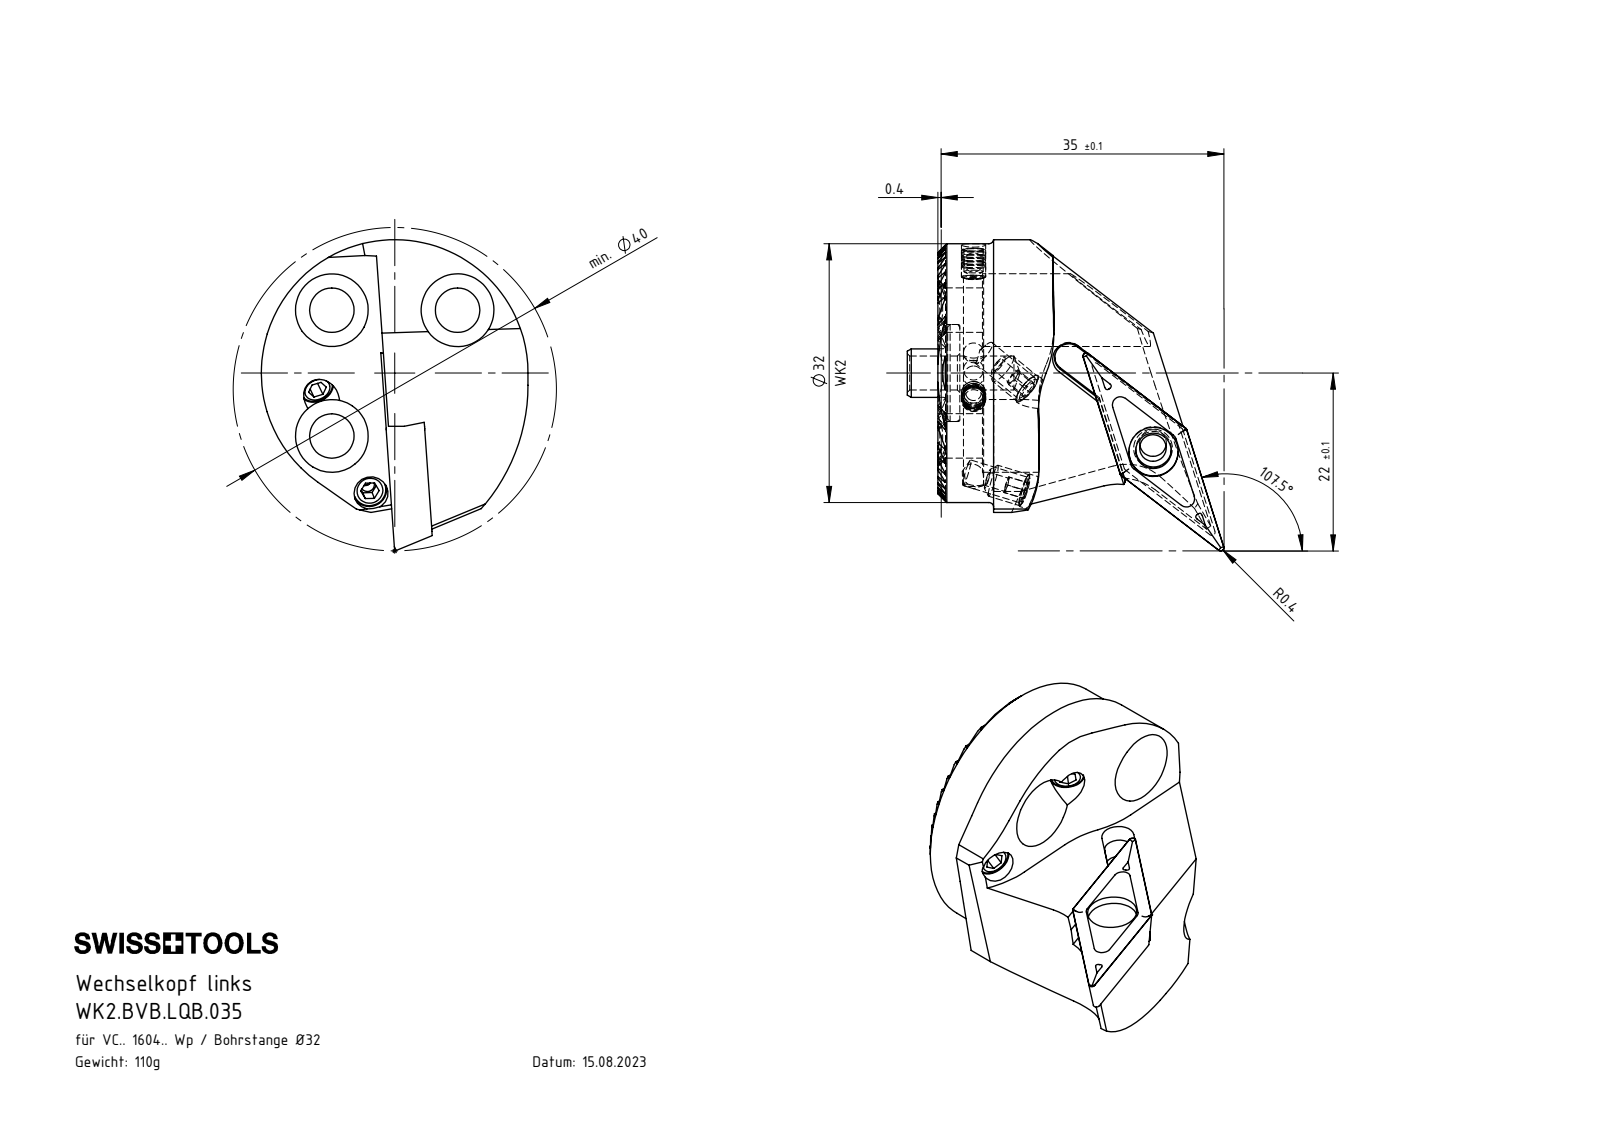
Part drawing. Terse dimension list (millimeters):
name: WK2-BVB.LQB.035_A; WK2-ER1.001.012_A_Fertigbearbeitung; KVT_MB_600_030; VCMT160404 (+2 more)
written by: SolidWorks 2017 (AUTOMOTIVE_DESIGN)
unit: mm
bodies: 9 solids, 496 faces (196 planar, 163 cylindrical, 137 other)
size: 39.2 × 38.5 × 33
volume: 13 572 mm³; area: 7 760 mm²
holes: 3× ⌀3.3, 3× ⌀4.2, 3× ⌀5.5, 3× ⌀9, 2× ⌀1.7, 2× ⌀2.38, 2× ⌀2.5, 2× ⌀3, 1× ⌀4.4, 1× ⌀6.1, 1× ⌀12
bosses: 2× ⌀4, 2× ⌀3, 1× ⌀32, 1× ⌀6
rounds: 22× R0.12, 3× R12, 1× R1.75, 1× R7, 1× R16.5, 1× R23
face distances: 1.3, 2.6, 3.9, 5.2, 6.5, 12.99, 11.69, 14.29, 7.8, 10.39
hole spacings: 11, 15.56, 22.01
